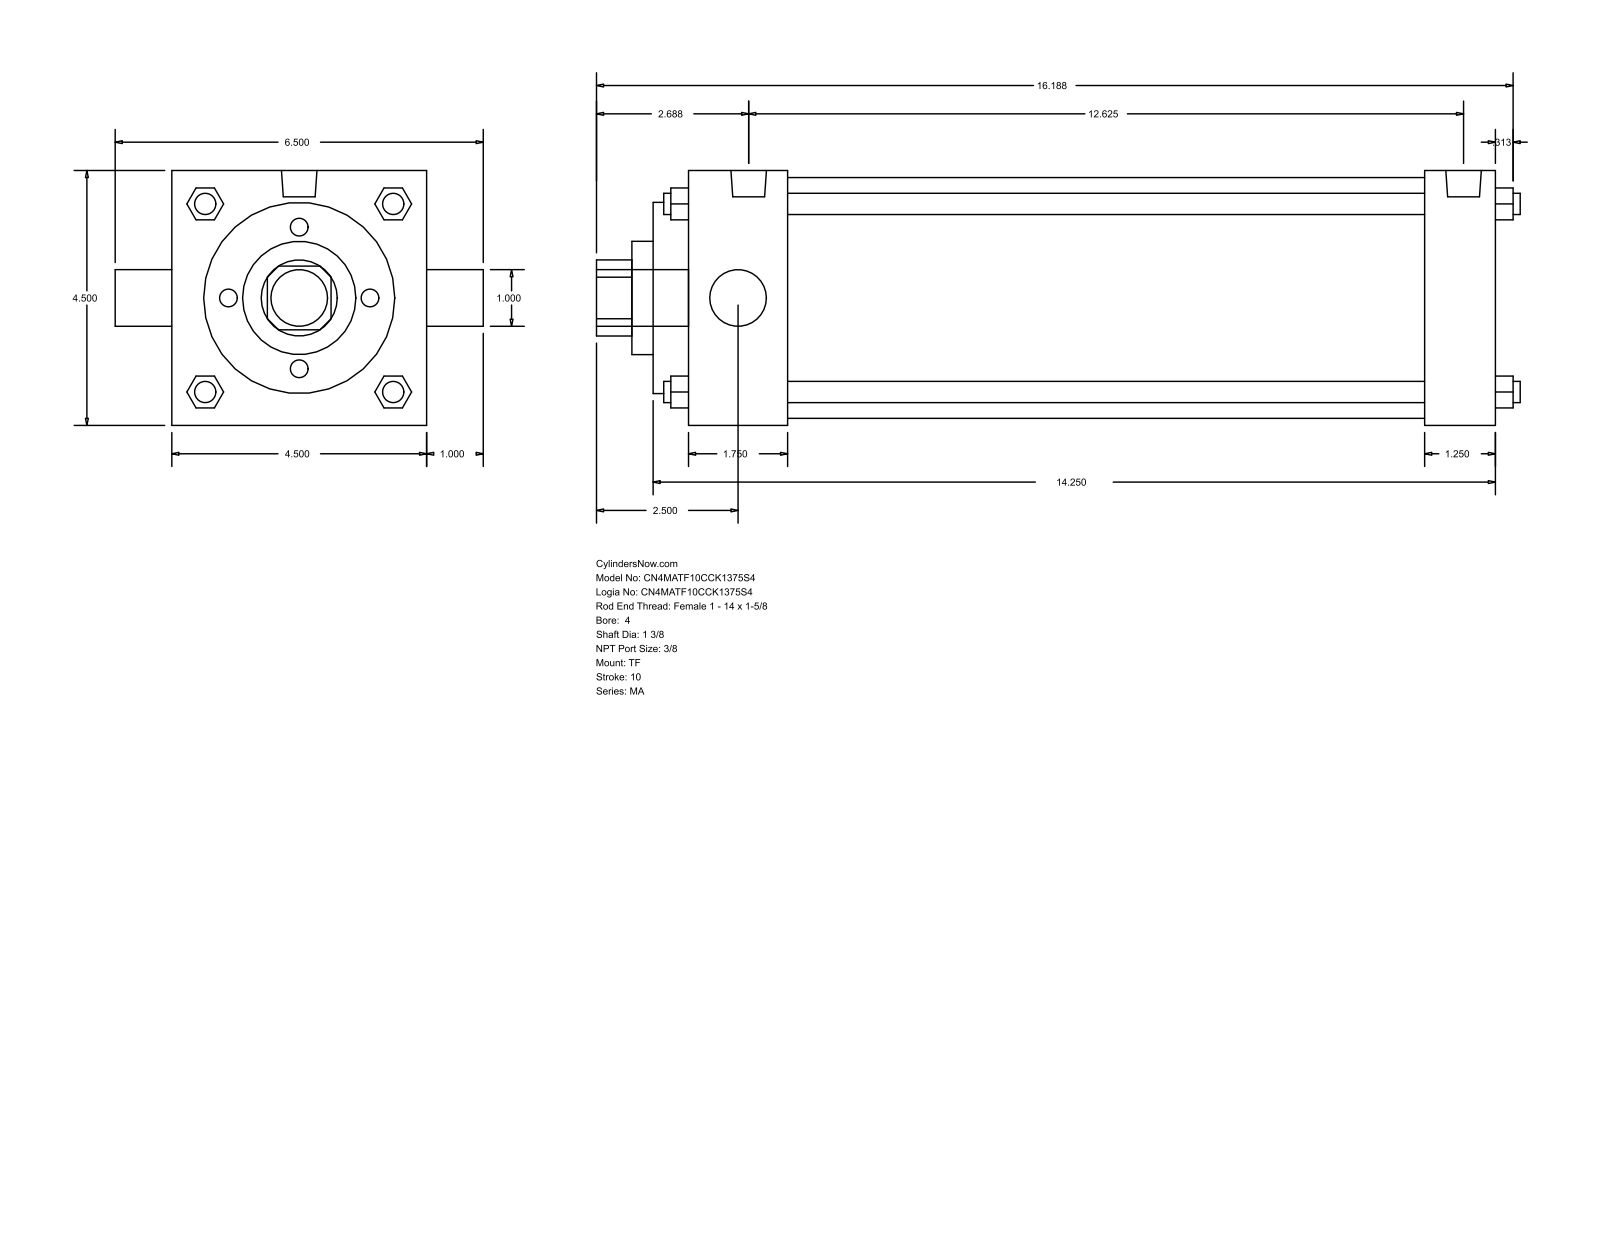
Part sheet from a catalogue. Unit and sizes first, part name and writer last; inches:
Units: inches
Overall size (bounding box): 16.313 × 6.5 × 4.5
Round holes (diameter × count): ⌀1 ×1, ⌀1.375 ×1, ⌀2 ×1, ⌀3.375 ×1, ⌀4.25 ×1
Round bosses / shafts (diameter × count): ⌀0.375 ×4, ⌀0.437 ×3, ⌀0.627 ×2, ⌀1 ×1
Partial cylindrical surfaces — rounded edges, fillets, slot ends (radius × count): R0.672 ×1
Main face-to-face distances: 4.5, 14.25, 0.625, 14.875, 13.625, 13, 1.25, 2.375, 1.75, 11.25
Bodies: 0 solids, 122 faces (93 planar, 29 cylindrical, 0 other)
Part name (STEP PRODUCT): MA_TF__0400_1.375
STEP written by: GSSL Pune (CONFIG_CONTROL_DESIGN)
